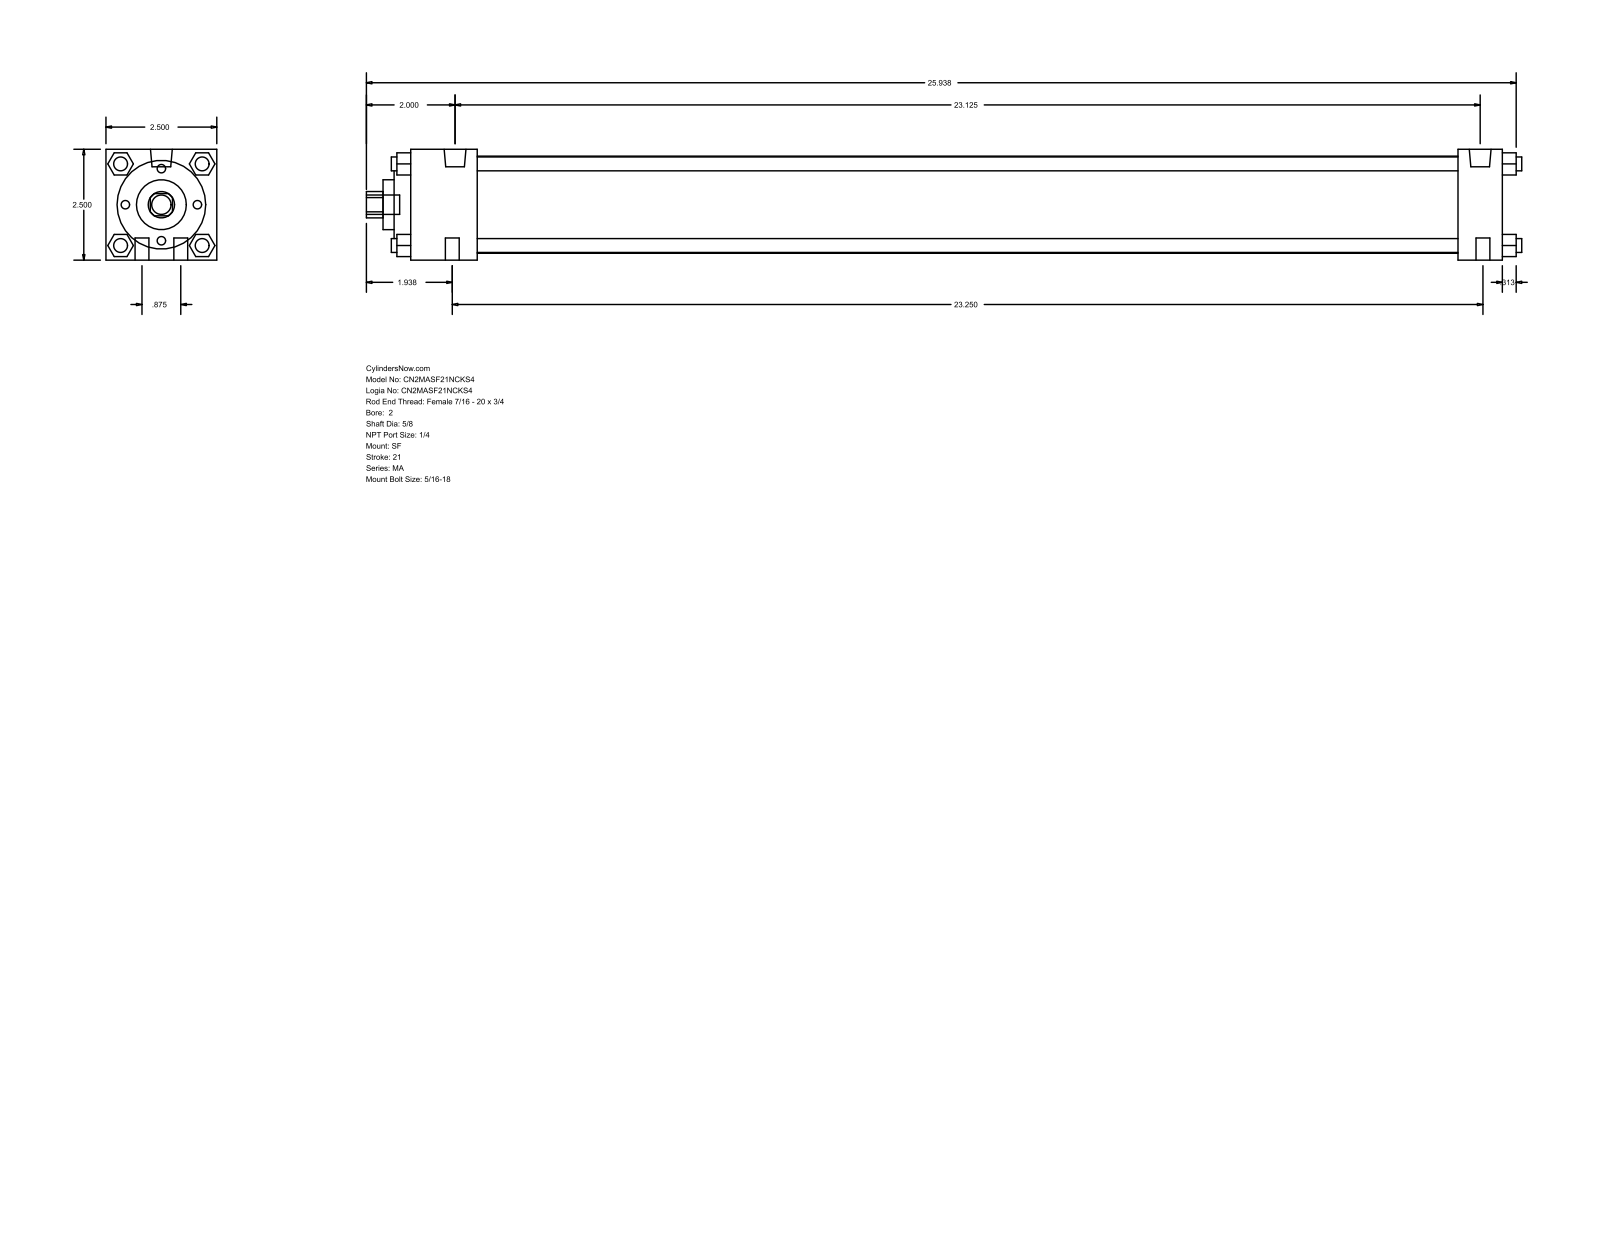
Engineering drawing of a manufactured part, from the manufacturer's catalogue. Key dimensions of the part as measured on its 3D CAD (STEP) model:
Part name (STEP PRODUCT): MA_SF__0200_0.625
STEP written by: GSSL Pune (CONFIG_CONTROL_DESIGN)
Units: millimetres
Bodies: 0 solids, 126 faces (95 planar, 31 cylindrical, 0 other)
Overall size (bounding box): 661.99 × 63.5 × 63.5
Round holes (diameter × count): ⌀15.88 ×1, ⌀28.57 ×1, ⌀50.8 ×1, ⌀55.63 ×1
Round bosses / shafts (diameter × count): ⌀7.94 ×10, ⌀12.49 ×2, ⌀11.11 ×1
Partial cylindrical surfaces — rounded edges, fillets, slot ends (radius × count): R7.54 ×1
Main face-to-face distances: 63.5, 12.7, 25.4, 38.1, 625.48, 9.52, 600.08, 561.98, 587.38, 47.62
